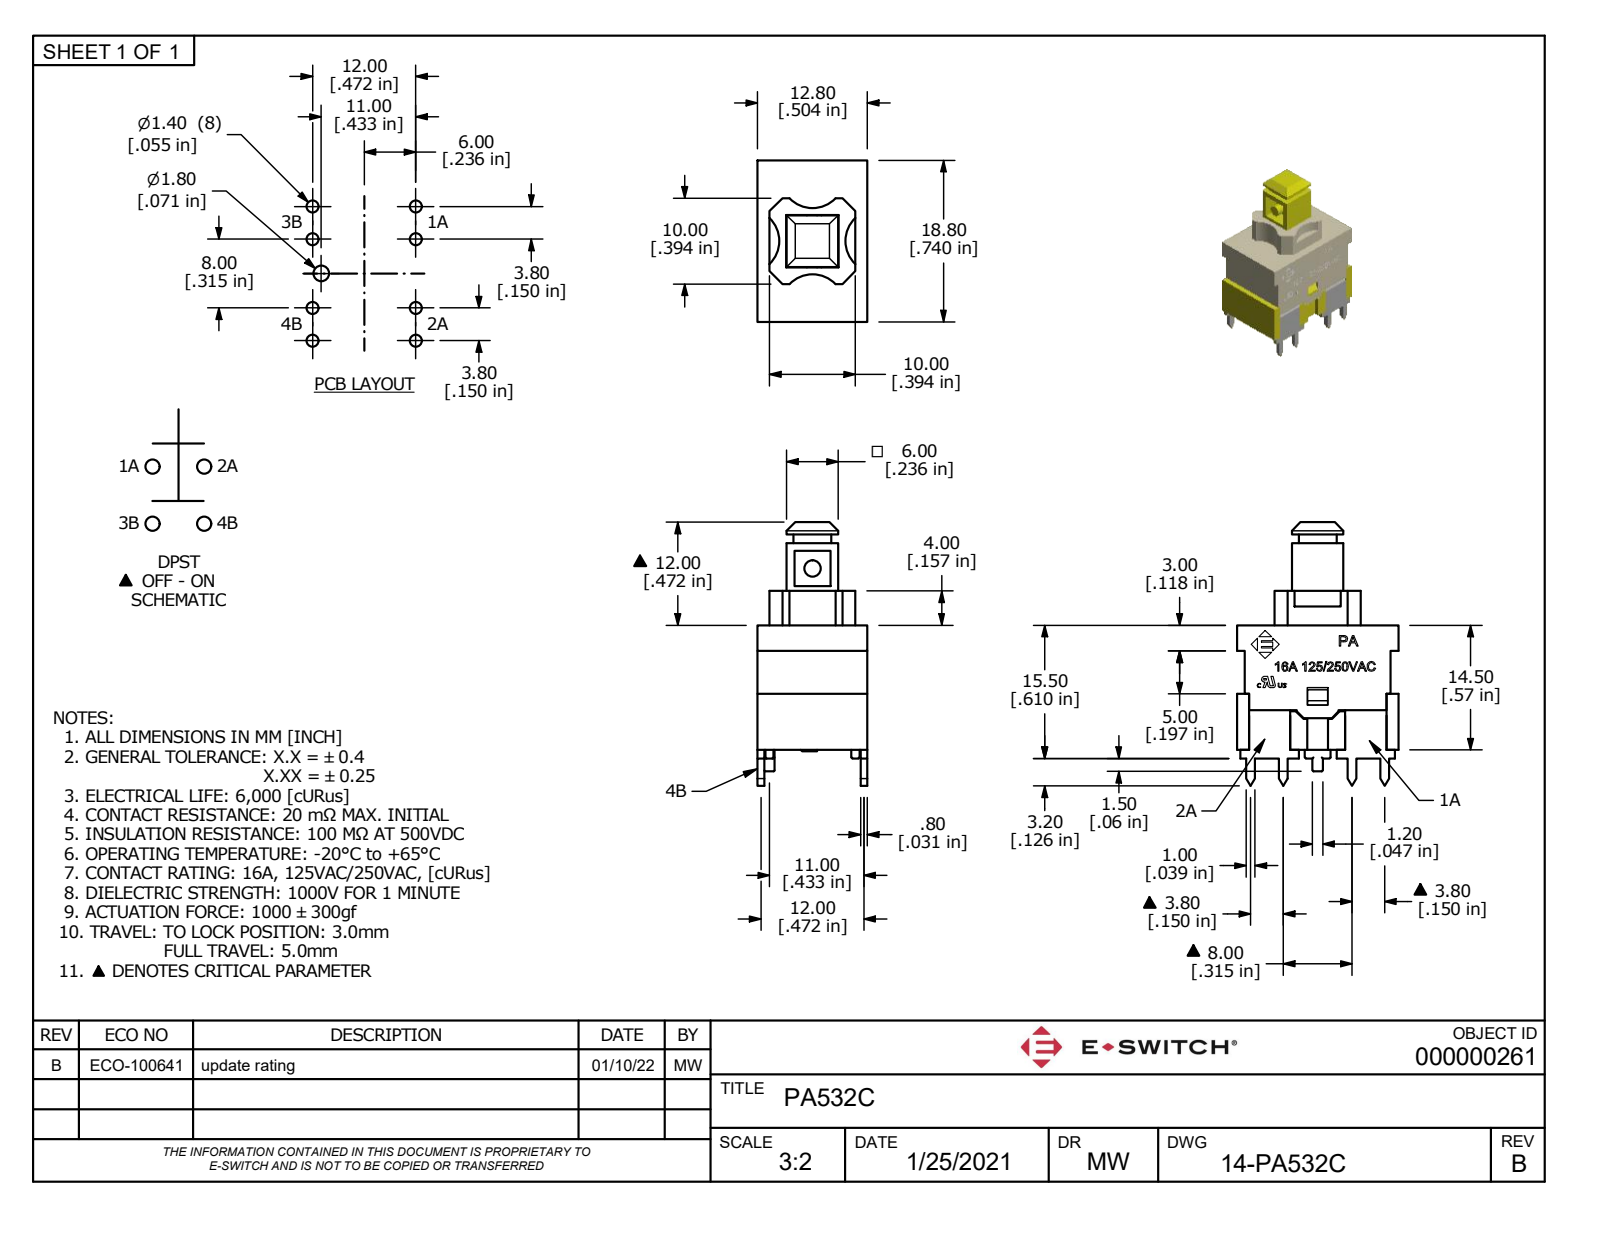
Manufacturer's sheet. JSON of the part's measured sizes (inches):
{"part_name": "PA532C", "step_written_by": "Autodesk Inventor 2022 (AUTOMOTIVE_DESIGN)", "units": "inches", "bodies": {"solids": 1, "faces": 869, "planar": 656, "cylindrical": 82, "other": 131}, "overall_size": [1.209, 0.74, 0.504], "volume_in3": 0.134, "surface_area_in2": 6.8, "round_holes": [[0.047, 2], [0.118, 1]], "round_bosses_or_shafts": [[0.037, 4], [0.098, 2], [0.075, 1]], "partial_cylinders_radius": [[0.01, 22], [0.005, 16], [0.006, 8], [0.039, 5], [0.146, 4], [0.02, 1], [0.024, 1], [0.07, 1]], "face_to_face_distances": [0.031, 0.472, 0.035, 0.661, 0.504, 0.079, 0.043, 0.339, 0.173, 0.039], "hole_center_spacings": [0.465]}
